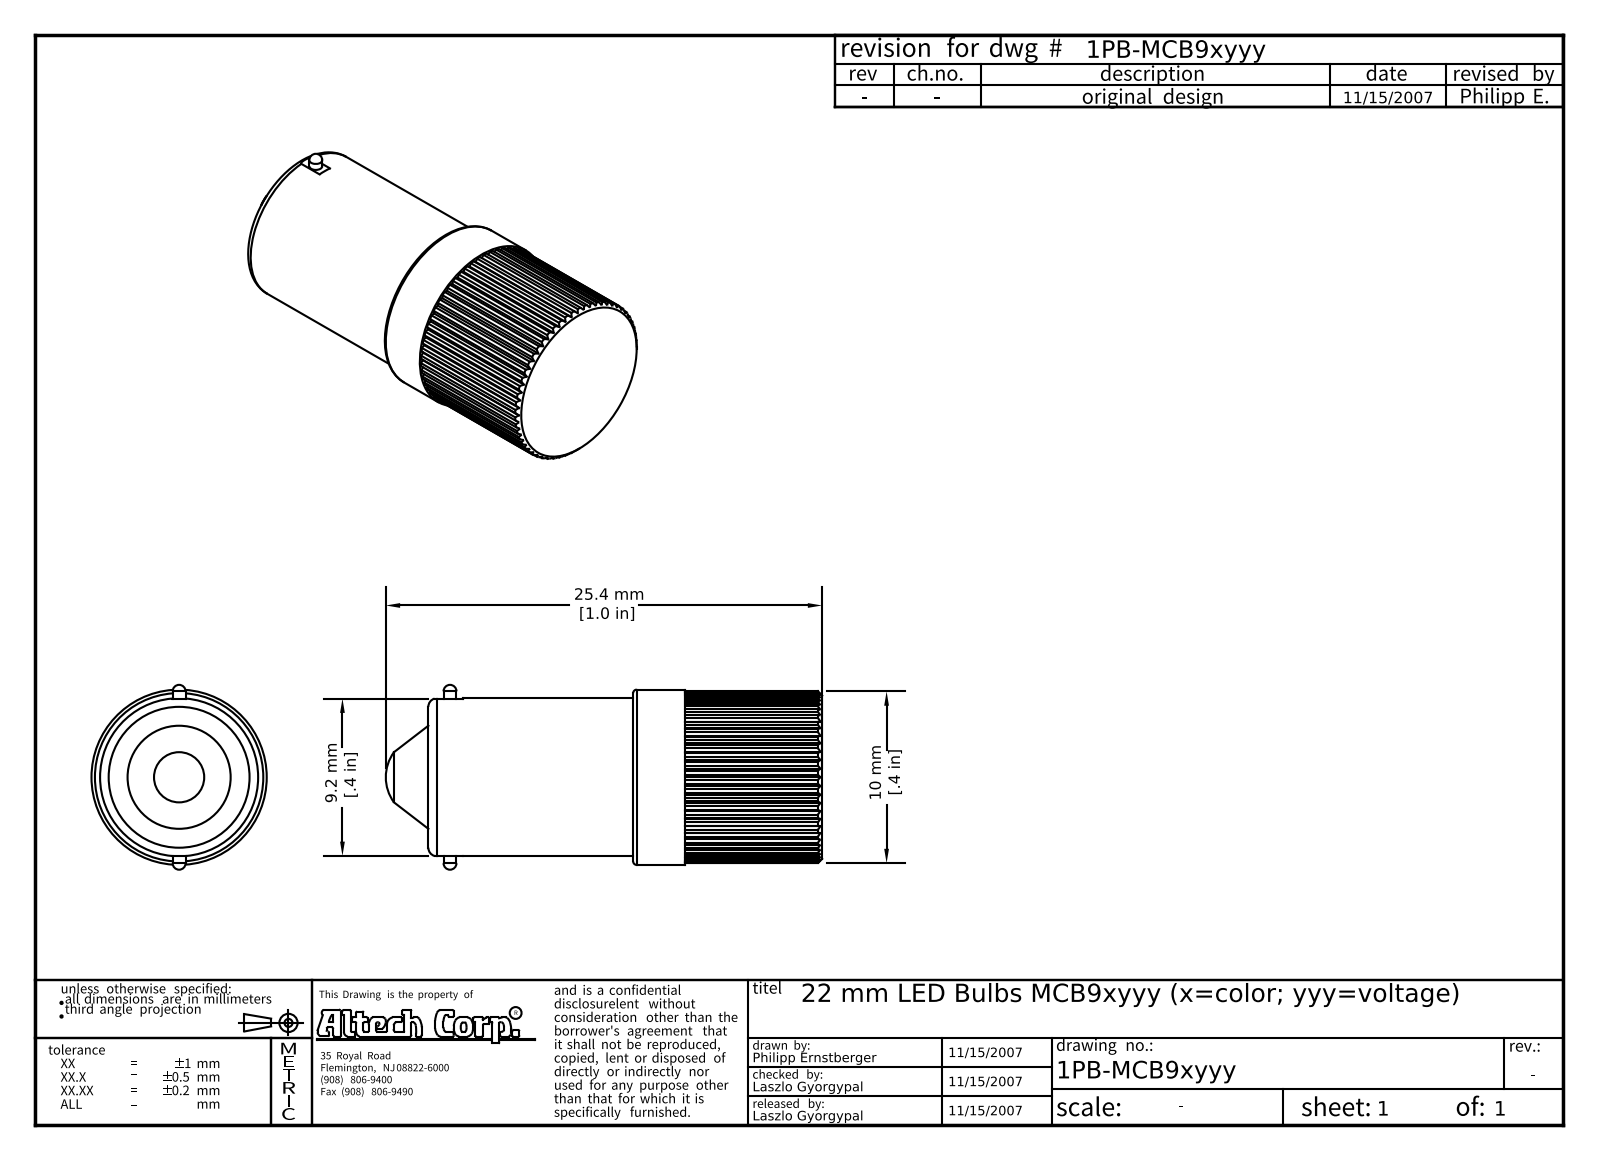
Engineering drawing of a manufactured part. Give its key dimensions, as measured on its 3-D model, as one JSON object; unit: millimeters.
{"part_name": "MCB9xxx", "step_written_by": "Autodesk Inventor 2008 (AUTOMOTIVE_DESIGN)", "units": "millimeters", "bodies": {"solids": 1, "faces": 199, "planar": 128, "cylindrical": 63, "other": 8}, "overall_size": [25.4, 10.76, 10.2], "volume_mm3": 1688, "surface_area_mm2": 917, "round_bosses_or_shafts": [[10.2, 1], [9.2, 1], [0.75, 1]], "partial_cylinders_radius": [[5, 1]], "face_to_face_distances": [6.86, 22.93, 6.85, 6.87, 11.93, 11, 14.93, 3, 8, 9.16]}
